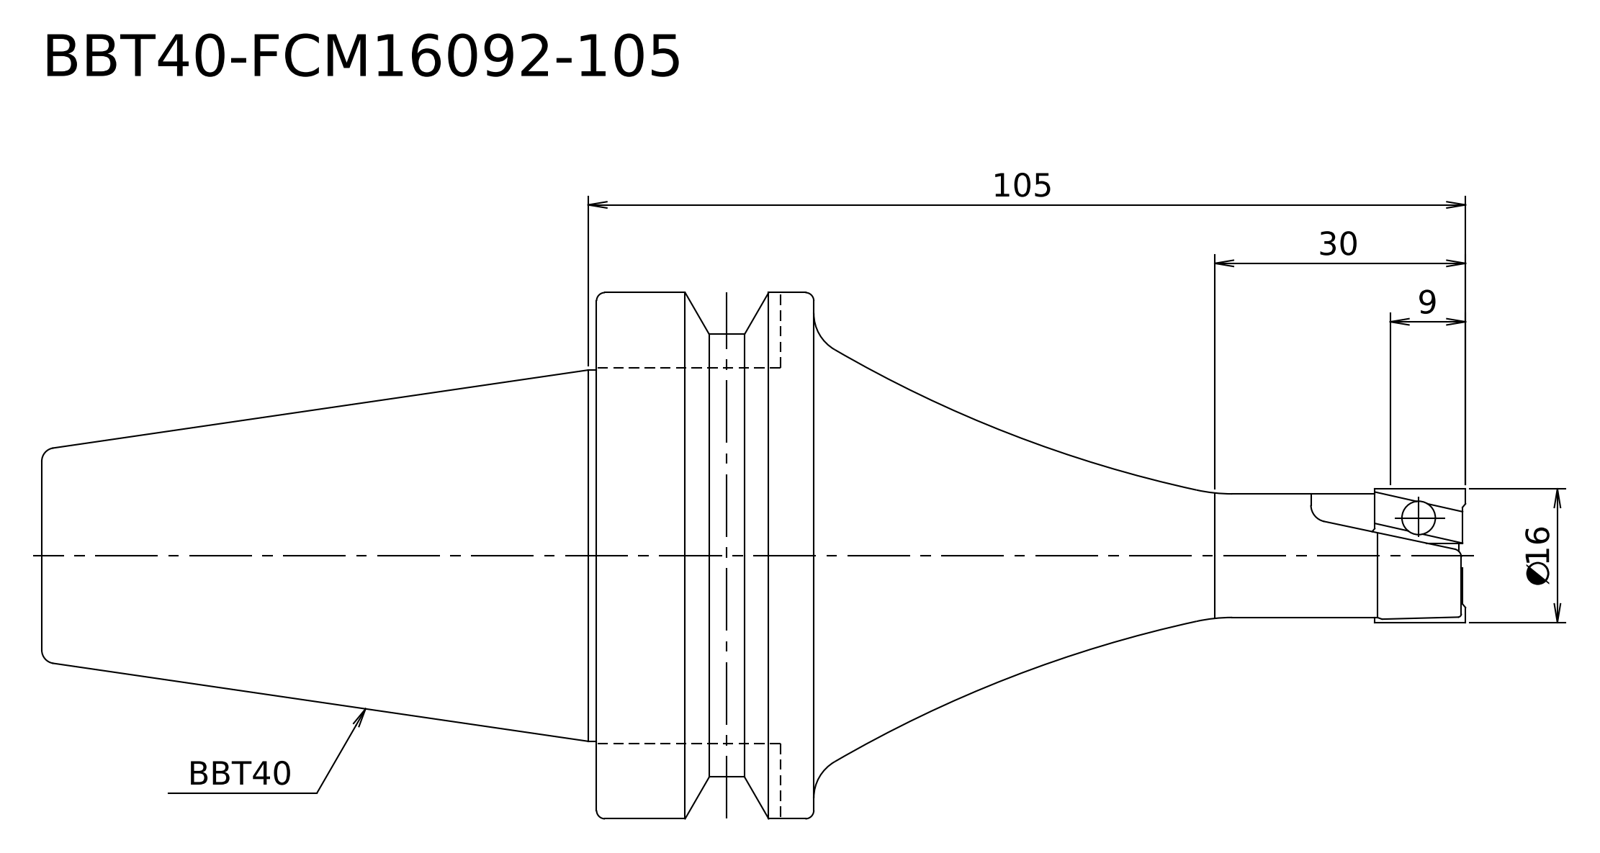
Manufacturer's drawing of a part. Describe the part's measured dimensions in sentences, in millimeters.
Its 3-D file was written by "Kubotek KeyCreator V8.5.1 (14335) (CONFIG_CONTROL_DESIGN)". It is 1 solid with 17 faces: 4 planar, 6 cylindrical and 7 other. Overall it measures 170.4 by 63 by 63 millimeters. Its volume is 190 950 cubic millimeters and its surface area 23 248 square millimeters. Round bosses or shafts: 1 of diameter 63, 1 of diameter 53, 1 of diameter 44.45, 1 of diameter 16, 1 of diameter 14.8. The main face-to-face distances are 66.4, 26, 92.4, 78, 104, 170.4.
